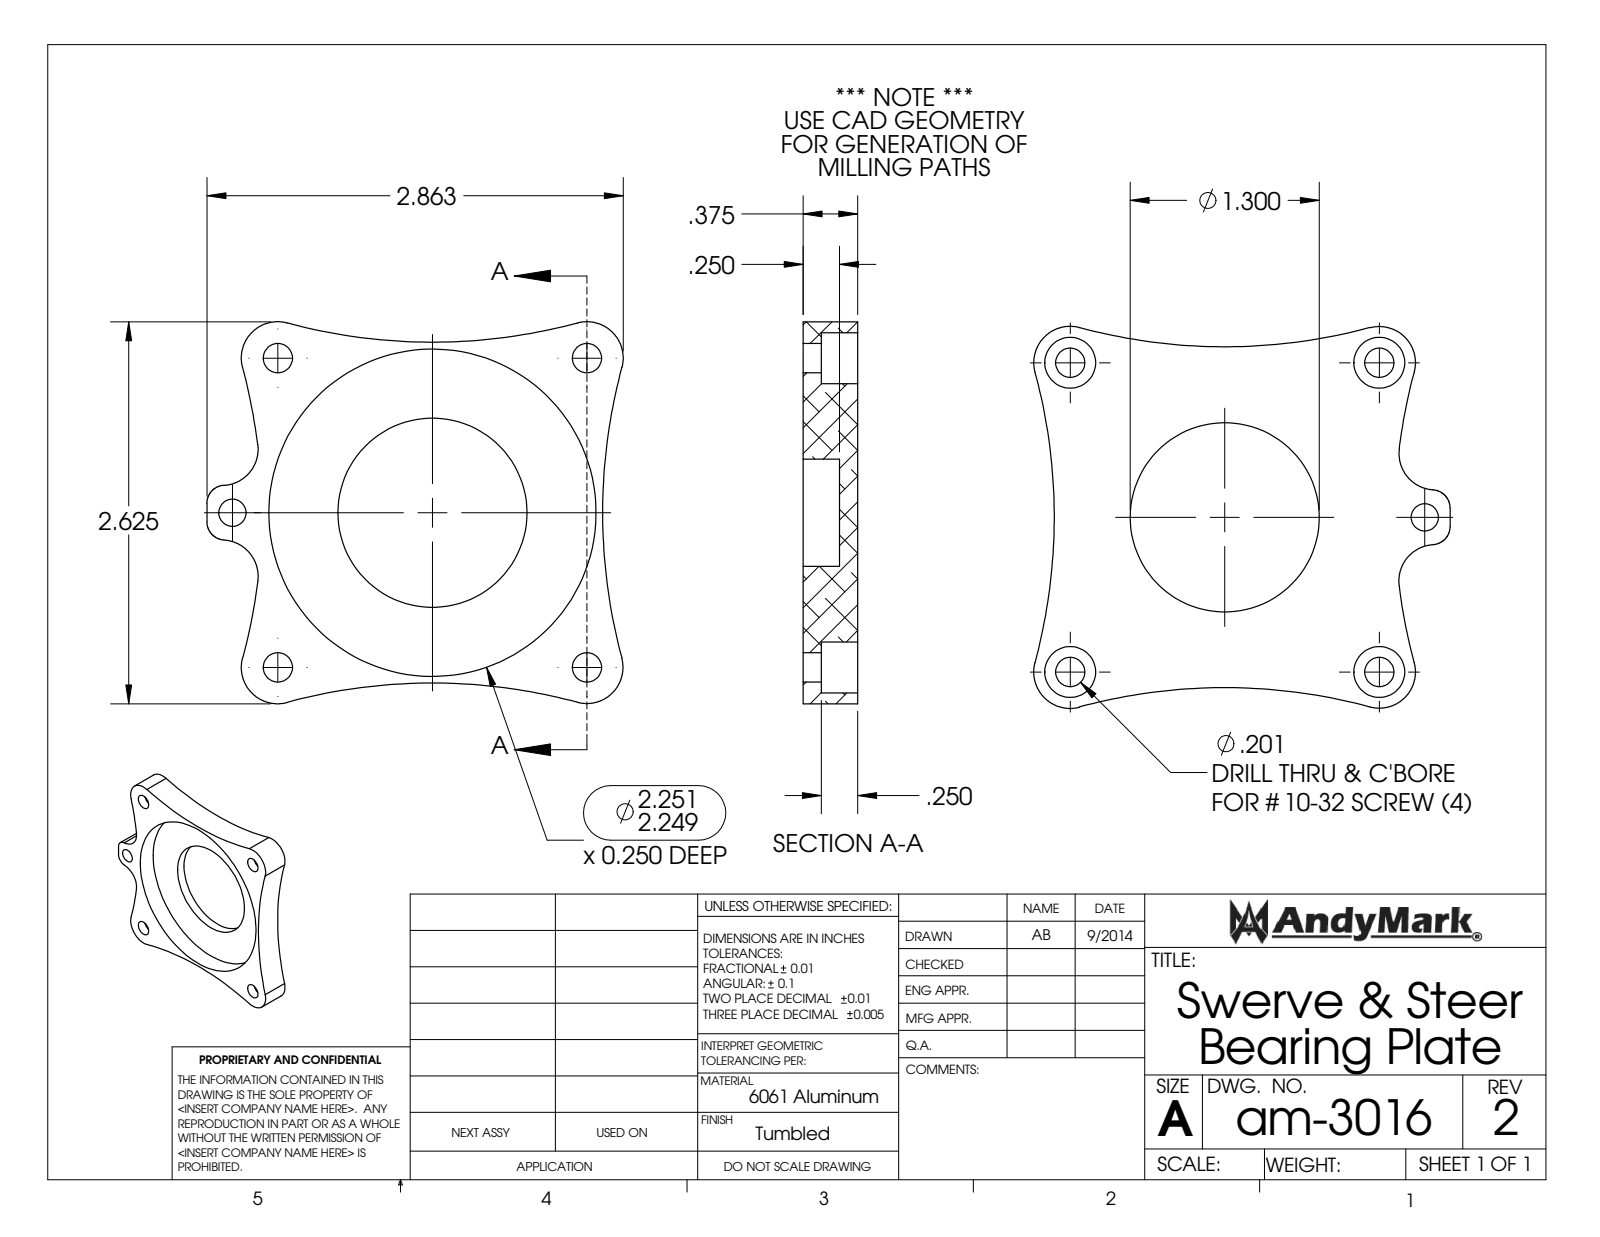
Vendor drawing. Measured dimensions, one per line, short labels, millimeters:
name: am-3016 S&S Bearing Plate
written by: SolidWorks 2014 (AUTOMOTIVE_DESIGN)
unit: mm
bodies: 1 solid, 46 faces (8 planar, 38 cylindrical, 0 other)
size: 72.7 × 66.7 × 9.5
volume: 17 270 mm³; area: 11 200 mm²
holes: 4× ⌀5.1, 4× ⌀8.9, 1× ⌀4.7, 1× ⌀33, 1× ⌀57.2
rounds: 6× R6.4, 4× R97.2, 2× R3.2
face distances: 3.2, 6.4, 9.5, 3.2
hole spacings: 38.2, 54, 67.5, 76.3, 28.1, 28.1, 34.9, 38.2
